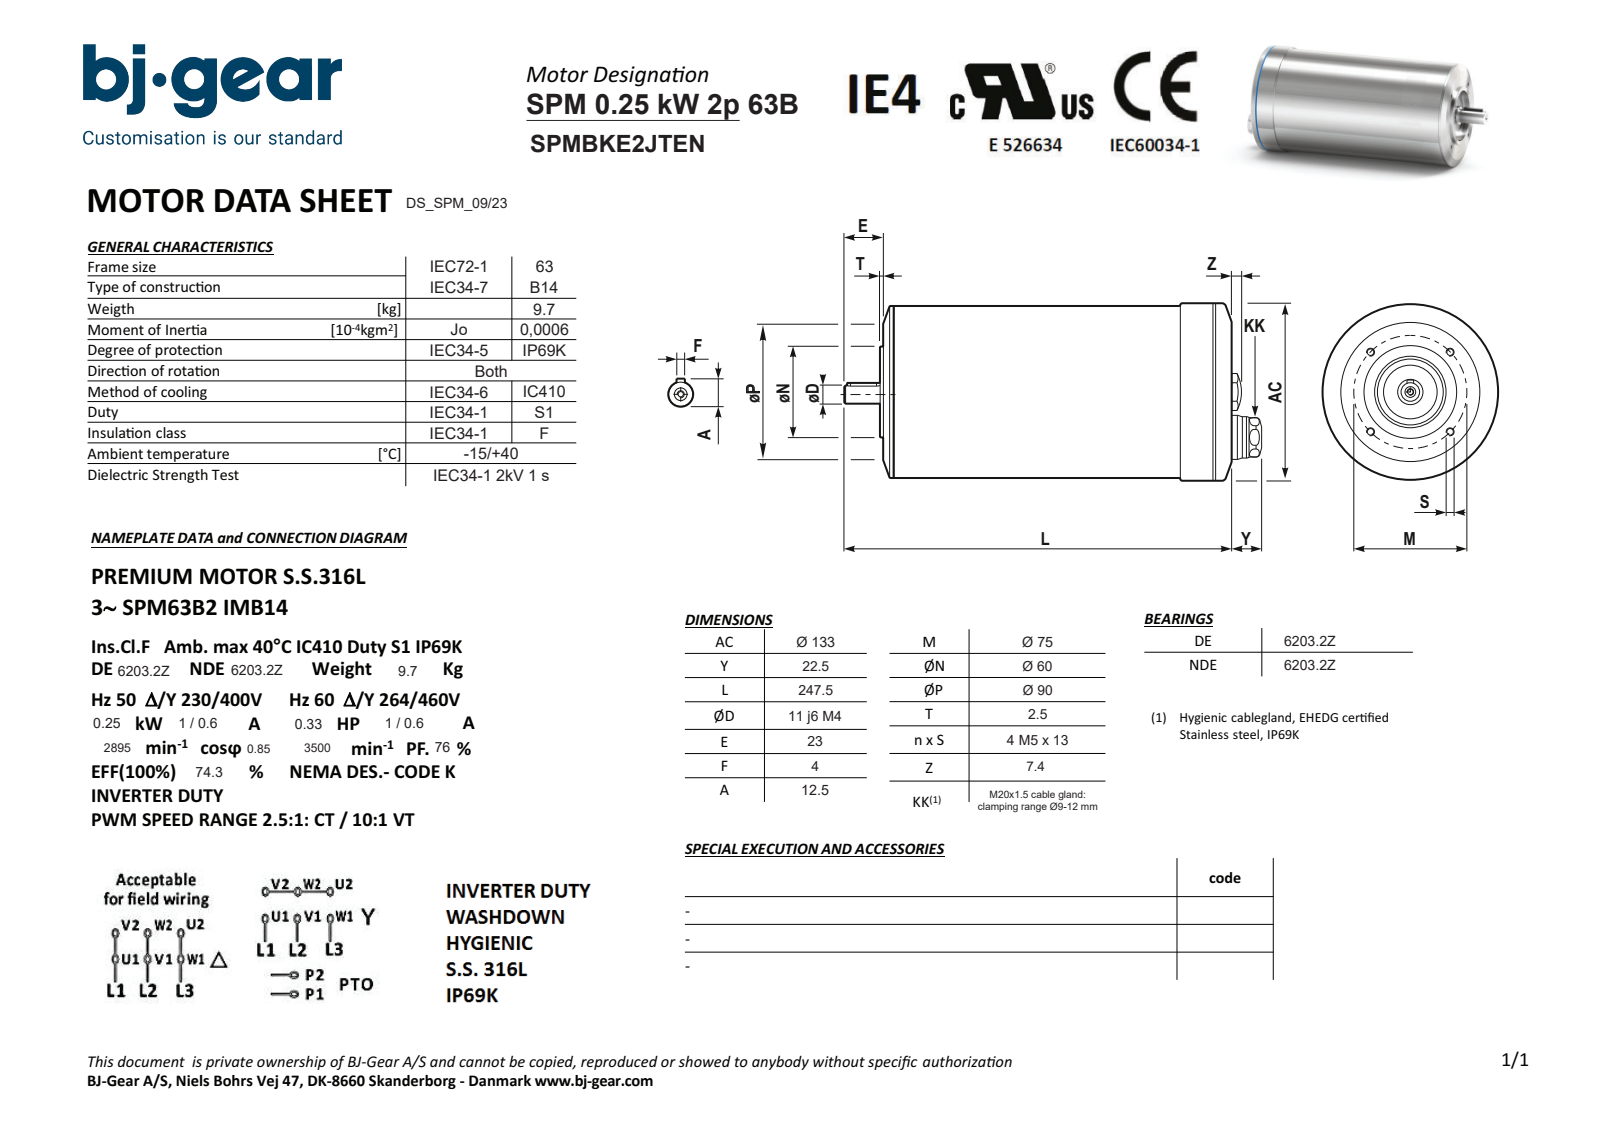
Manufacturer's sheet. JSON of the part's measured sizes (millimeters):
{"part_name": "SPMBKE2JTENN4KSA1-N---NNN", "step_written_by": "Solid Edge (AUTOMOTIVE_DESIGN)", "units": "millimeters", "bodies": {"solids": 1, "faces": 87, "planar": 30, "cylindrical": 32, "other": 25}, "overall_size": [275, 133, 133], "volume_mm3": 2939000, "surface_area_mm2": 120931, "round_holes": [[4.13, 4], [3.24, 1], [4.3, 1], [7, 1], [13.4, 1], [52, 1]], "round_bosses_or_shafts": [[133, 1], [132.98, 1], [129, 1], [128.98, 1], [60, 1], [20, 1], [17, 1], [11, 1]], "partial_cylinders_radius": [[2, 2], [12.8, 1]], "face_to_face_distances": [224.5, 219, 5.5, 2.5, 8, 227, 24, 12, 231, 236.5], "hole_center_spacings": [37.5, 53.04, 27.55, 66.08, 75.01, 34]}
